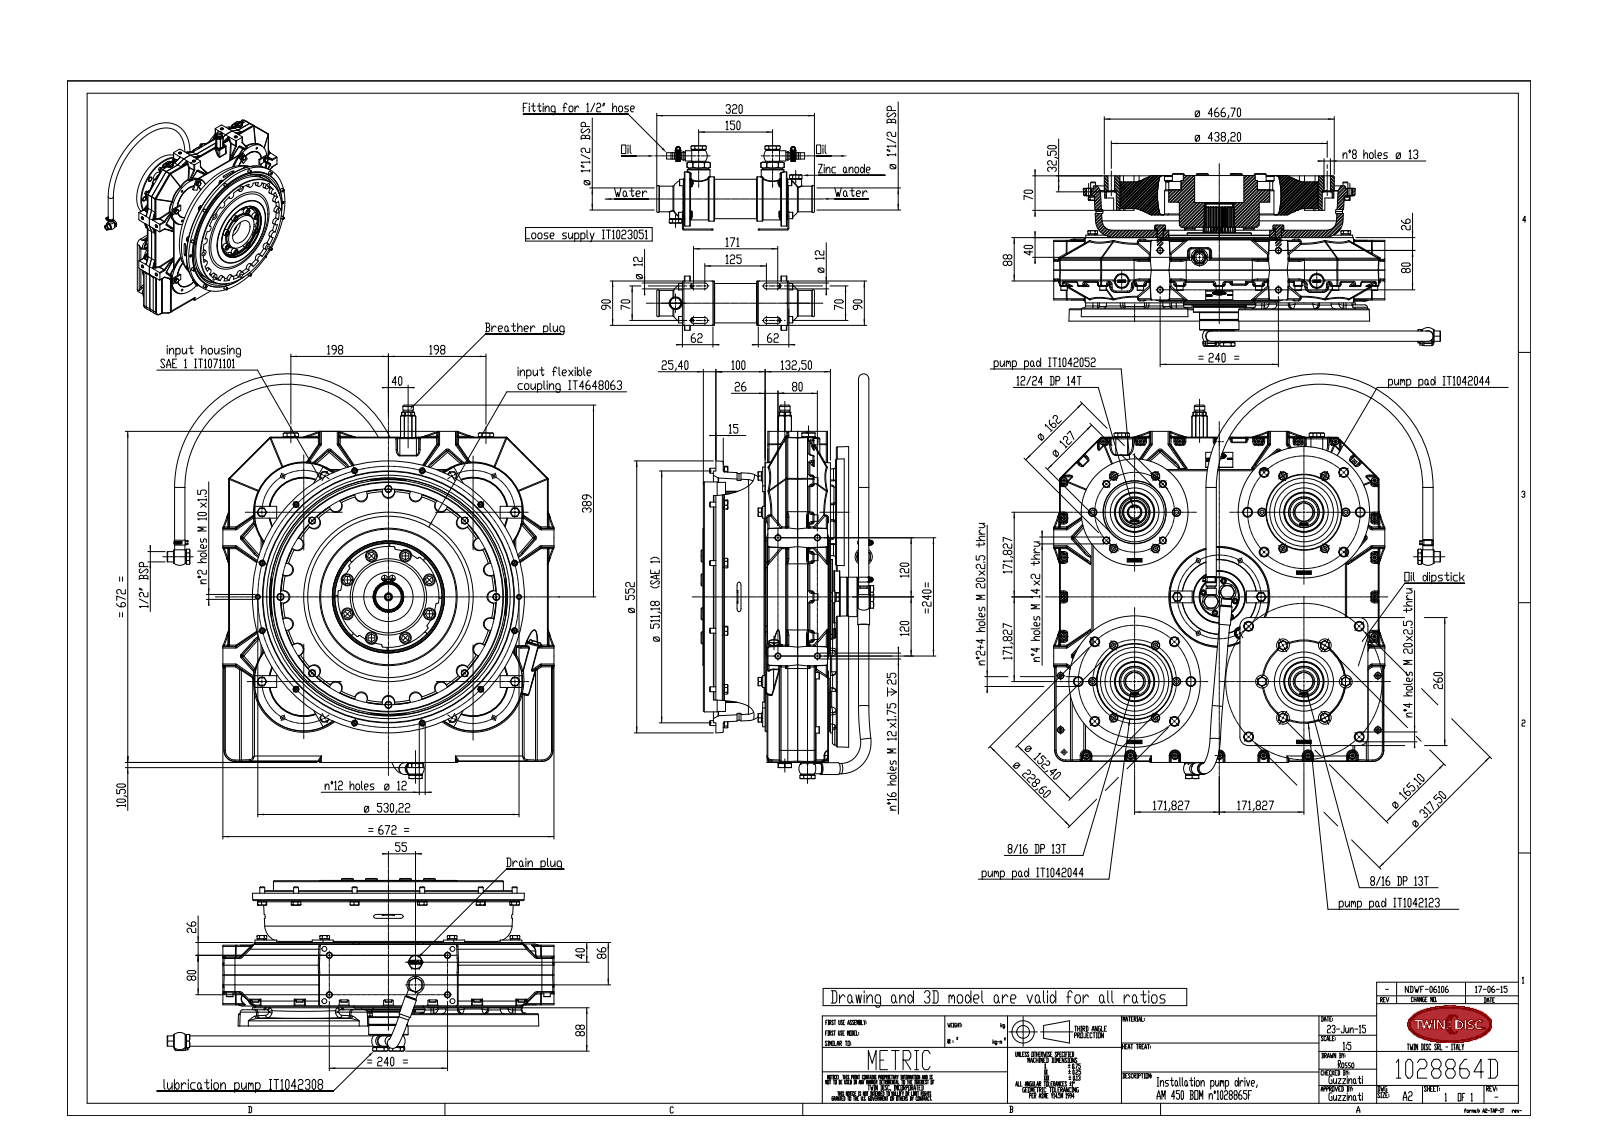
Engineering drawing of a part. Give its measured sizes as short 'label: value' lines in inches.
name: IT1042308_A_rev01-installation; IT1042123_rev01-installation; IT2021216_rev03-installation; IT4588040_rev00-installation (+8 more)
written by: SolidWorks 2007 (AUTOMOTIVE_DESIGN)
unit: in
bodies: 160 solids, 14327 faces (5564 planar, 4459 cylindrical, 4304 other)
size: 47.372 × 32.35 × 23.263
volume: 1 455 in³; area: 10 200 in²
holes: 70× ⌀0.335, 38× ⌀0.402, 33× ⌀0.433, 28× ⌀0.472, 26× ⌀0.669, 25× ⌀0.512, 18× ⌀0.689, 17× ⌀0.551, 14× ⌀0.315, 13× ⌀0.827, 12× ⌀0.394, 7× ⌀0.63
bosses: 47× ⌀0.394, 32× ⌀0.512, 32× ⌀0.315, 28× ⌀0.638, 28× ⌀0.63, 23× ⌀0.713, 21× ⌀0.787, 12× ⌀0.945
rounds: 370× R0.098, 134× R0.079, 73× R0.492, 58× R0.018, 54× R0.039, 40× R0.197, 35× R0.059, 24× R0.315
face distances: 2.598, 5.059, 0.157, 1.614, 2.441, 0.591, 2.461, 4.902, 0.748, 5.65
hole spacings: 4.724, 1.865, 3.346, 7.023, 8.183, 9.567, 5.796, 9.449
